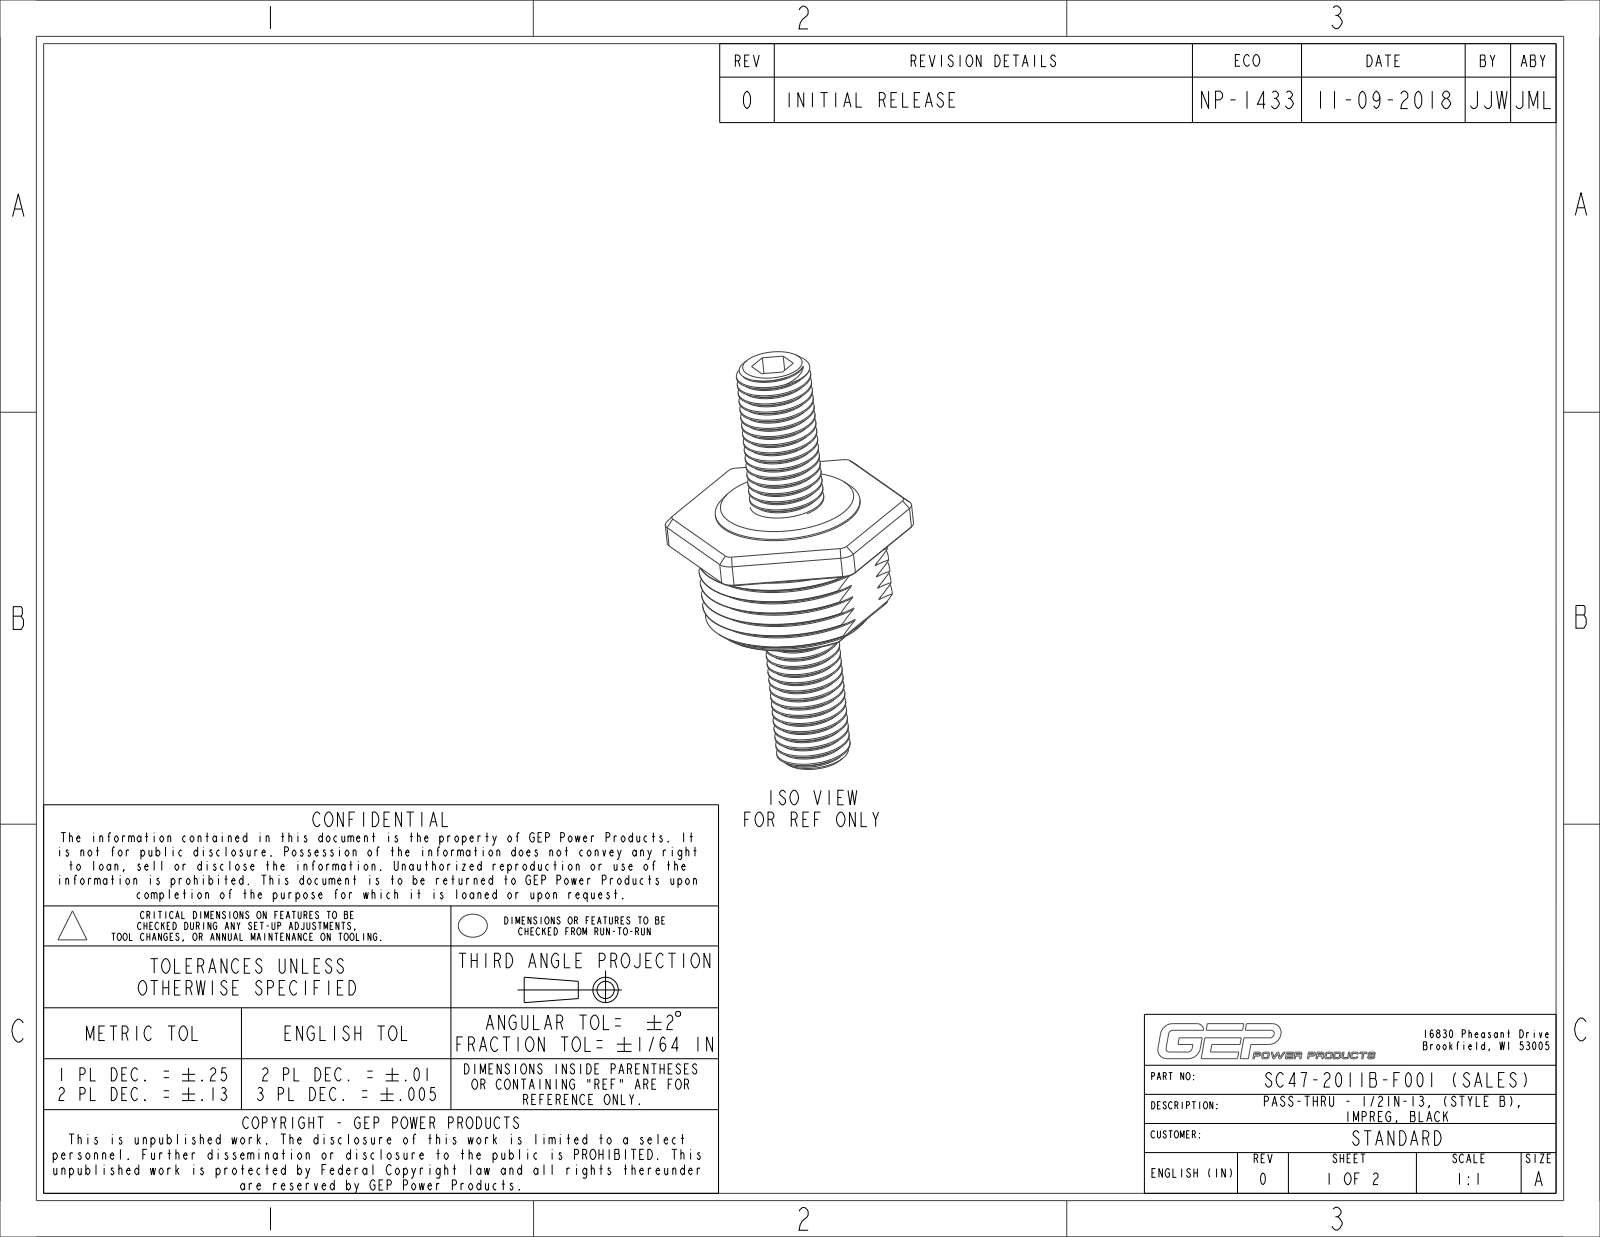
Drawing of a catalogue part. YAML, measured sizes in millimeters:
part_name: "SC47-2011B-F001_NCF_SW0001"
step_written_by: "CREO PARAMETRIC BY PTC INC, 2017110 (CONFIG_CONTROL_DESIGN)"
units: millimeters
bodies: {solids: 1, faces: 289, planar: 43, cylindrical: 106, other: 140}
overall_size: [76.2, 43.21, 38.1]
volume: 24259
surface_area: 9859
round_holes:
  - {diameter: 10.72, count: 1}
round_bosses_or_shafts:
  - {diameter: 25.4, count: 1}
  - {diameter: 12.95, count: 1}
partial_cylinders:
  - {radius: 2.54, count: 6}
  - {radius: 4.6, count: 6}
  - {radius: 0.76, count: 2}
  - {radius: 16.57, count: 1}
face_to_face_distances: [1.27, 21.59, 6.35, 5.08, 16.51, 22.86, 22.22, 15.88, 15.24, 38.1]
